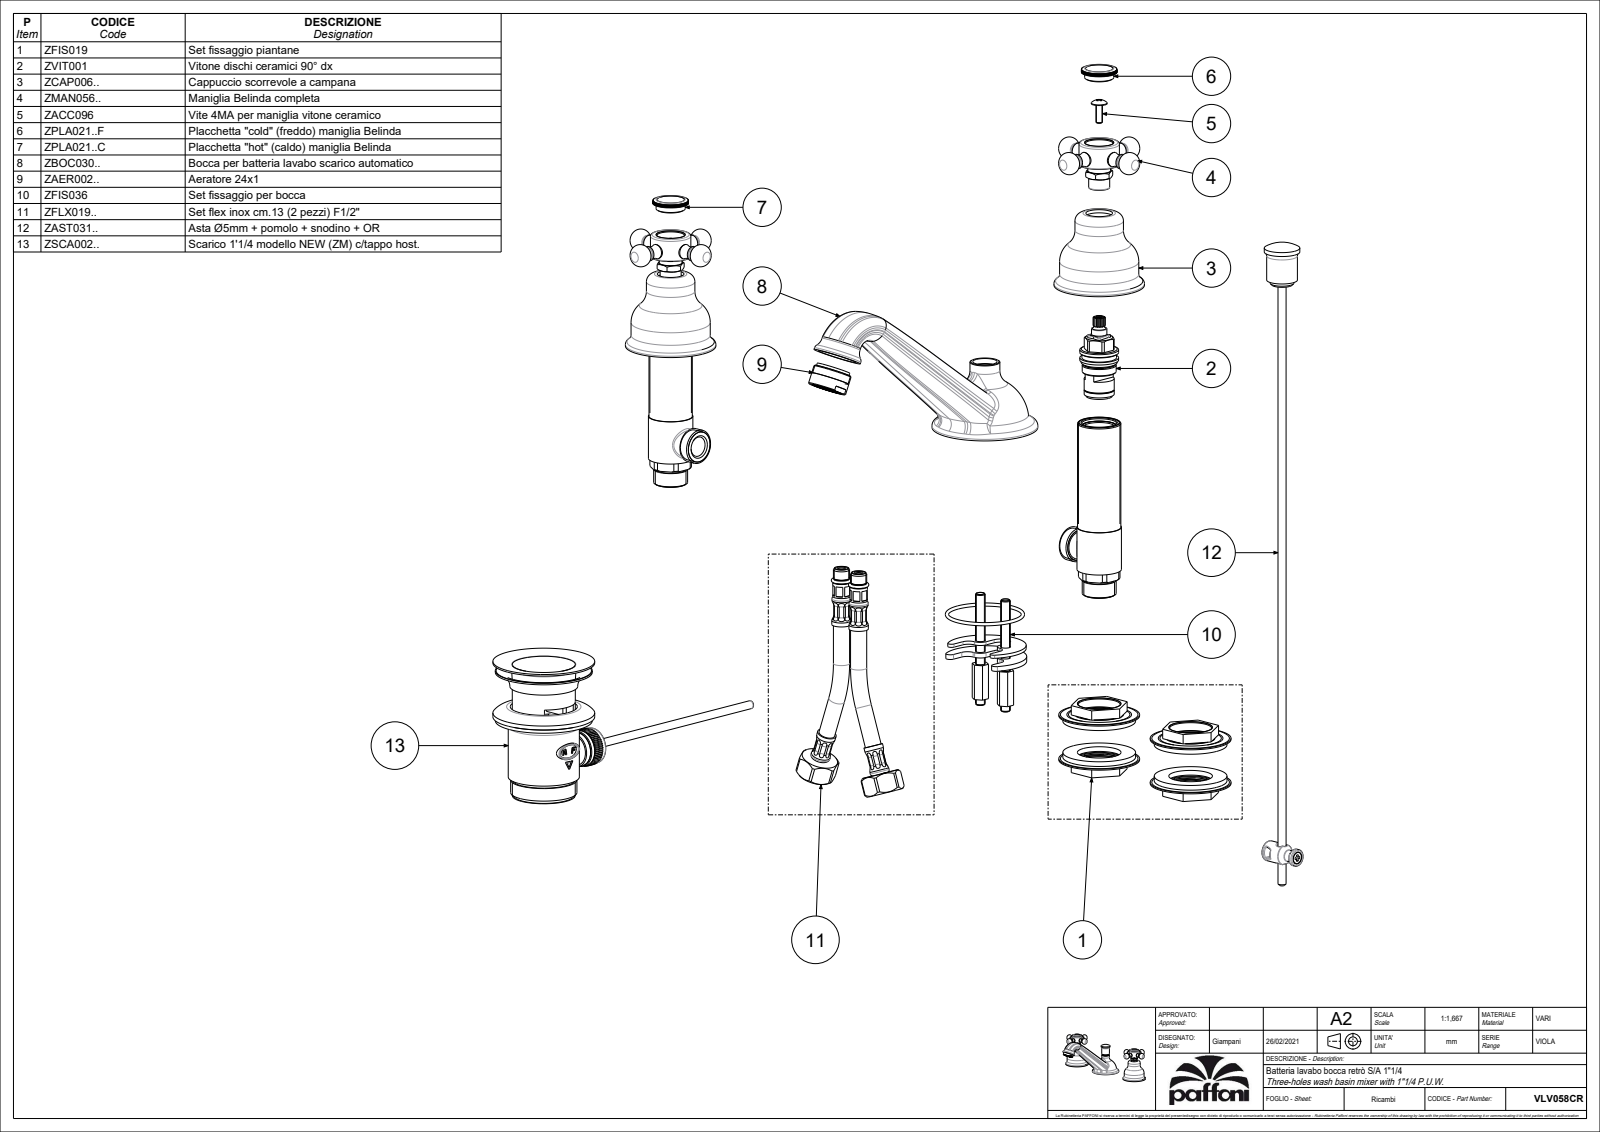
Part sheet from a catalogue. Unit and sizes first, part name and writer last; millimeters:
Units: millimetres
Overall size (bounding box): 264.07 × 175.97 × 94.3
Round bosses / shafts (diameter × count): ⌀9 ×3, ⌀7 ×3, ⌀55 ×2, ⌀49 ×2, ⌀28 ×2, ⌀25 ×2, ⌀24 ×2, ⌀14 ×2
Partial cylindrical surfaces — rounded edges, fillets, slot ends (radius × count): R11 ×2
Main face-to-face distances: 57.2, 7.7, 46.5, 10.7, 15, 42.8, 3.7, 14.4, 15.2, 3
Volume: 302 953 mm³ · Surface area: 53 633 mm²
Bodies: 3 solids, 998 faces (443 planar, 292 cylindrical, 263 other)
Part name (STEP PRODUCT): VLV058CR
STEP written by: CREO PARAMETRIC BY PTC INC, 2020044 (CONFIG_CONTROL_DESIGN)
